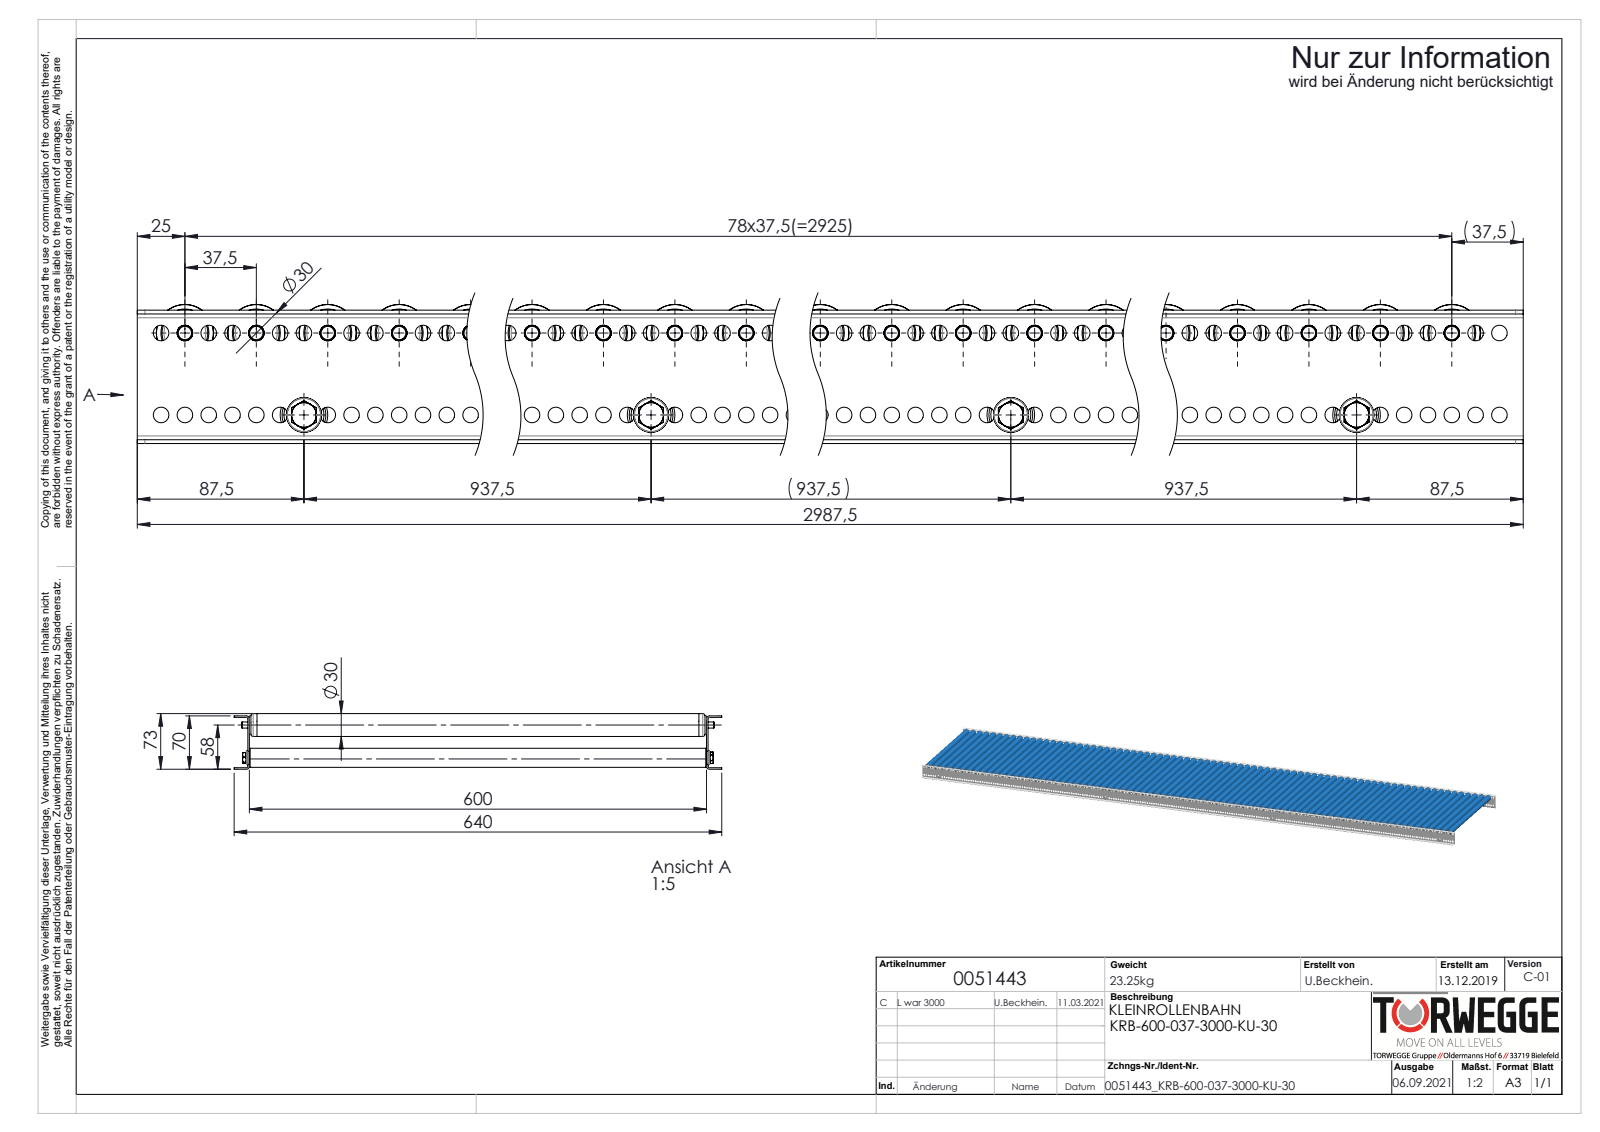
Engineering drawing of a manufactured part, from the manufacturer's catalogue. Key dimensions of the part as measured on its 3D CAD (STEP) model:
Part name (STEP PRODUCT): 0017013_Tragrollenrohr-Ø30x1,8KU_KFG_L=580; Profil_KRB-20x70x20x2_KFG_S109079_U-PROFIL-20-70-20-2-KRB-30-L=2987,5; S100994_Sperrzahnschraube_M08x16-8.8-A2K; S100995_TYP-KUT50-30x1,8-A8 (+4 more)
STEP written by: SolidWorks 2020 (AUTOMOTIVE_DESIGN)
Units: millimetres
Bodies: 180 solids, 18686 faces (5734 planar, 7056 cylindrical, 5896 other)
Overall size (bounding box): 2987.5 × 640 × 73
Volume: 11 310 000 mm³ · Surface area: 11 880 000 mm²
Round holes (diameter × count): ⌀8.2 ×476, ⌀8.1 ×79, ⌀22.6 ×79, ⌀25.2 ×79, ⌀6.8 ×4, ⌀21 ×4
Round bosses / shafts (diameter × count): ⌀8 ×83, ⌀30 ×79, ⌀29.9 ×79, ⌀26.5 ×79, ⌀26.4 ×79, ⌀24 ×79, ⌀25 ×4
Partial cylindrical surfaces — rounded edges, fillets, slot ends (radius × count): R5.05 ×79, R4 ×8, R2 ×4
Main face-to-face distances: 2, 602, 68, 600, 604, 70, 66, 10, 590, 12
Hole centre spacings: 12.5, 25, 37.5, 50, 62.5, 75, 87.5, 100
